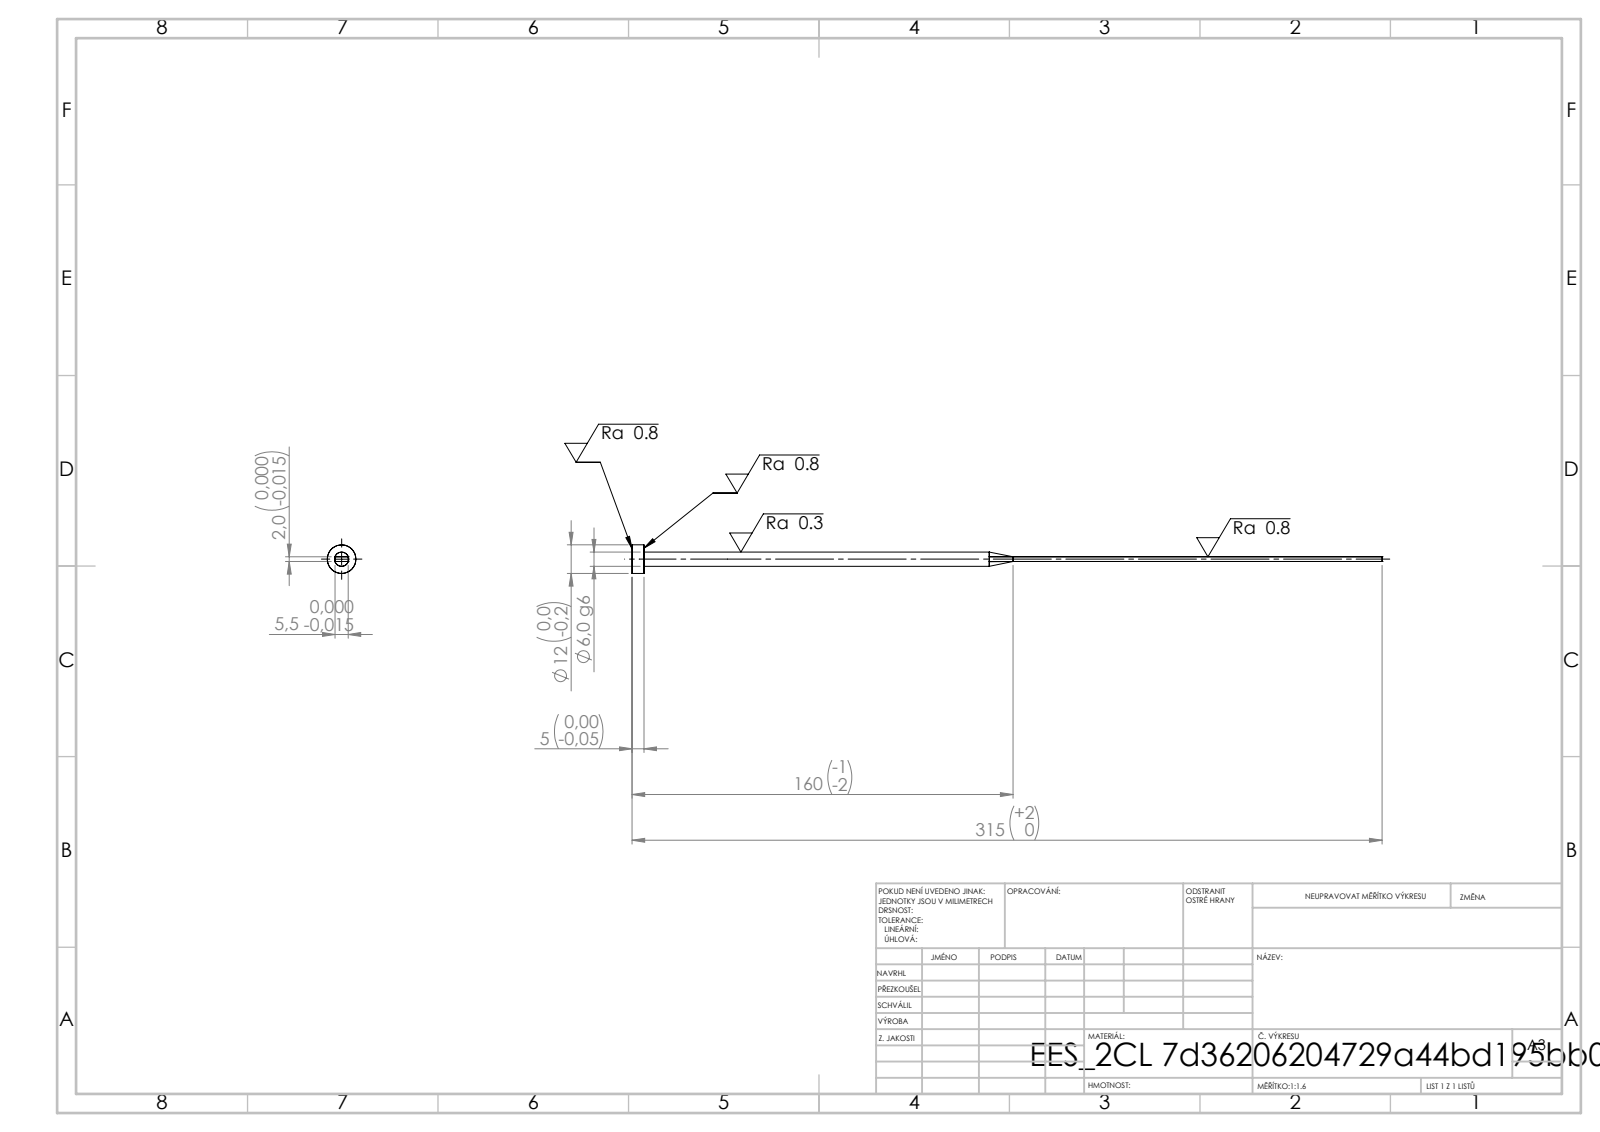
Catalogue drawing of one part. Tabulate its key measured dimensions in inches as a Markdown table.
| quantity | value |
| --- | --- |
| STEP written by | SolidWorks 2019 (CONFIG_CONTROL_DESIGN) |
| units | inches |
| bodies | 1 solid, 15 faces (7 planar, 4 cylindrical, 4 other) |
| overall size | 12.402 × 0.472 × 0.472 |
| volume | 0.4 in³ |
| surface area | 8.713 in² |
| round bosses / shafts (diameter × count) | 0.472 × 1, 0.236 × 1 |
| main face-to-face distances | 0.079, 0.217, 0.197, 12.402, 12.205 |
